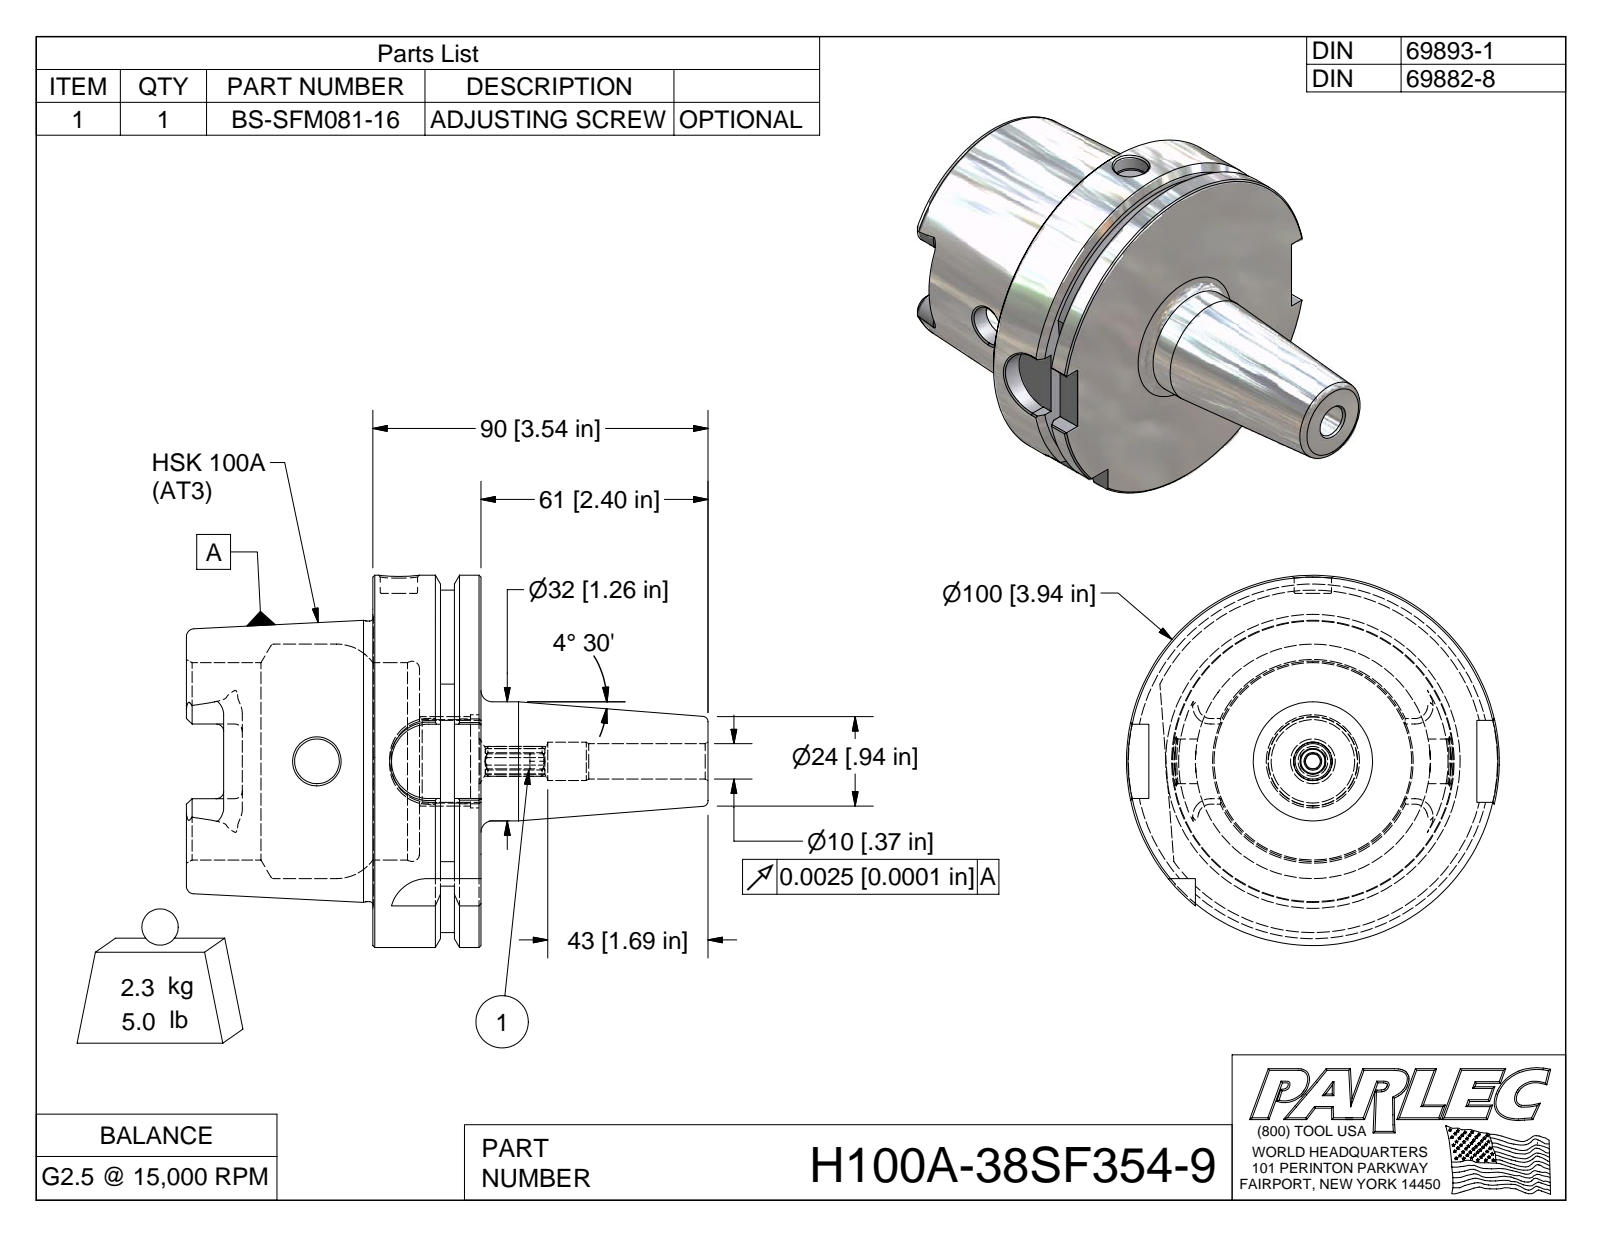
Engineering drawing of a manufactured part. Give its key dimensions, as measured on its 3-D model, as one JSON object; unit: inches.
{"part_name": "H100A-38SF354-9; H100A-38SF354-9-1; BS-SFM081-16", "step_written_by": "Autodesk Inventor 2009 (AUTOMOTIVE_DESIGN)", "units": "inches", "bodies": {"solids": 2, "faces": 149, "planar": 49, "cylindrical": 30, "other": 70}, "overall_size": [5.509, 3.937, 3.937], "volume_in3": 17.71, "surface_area_in2": 88.83, "round_holes": [[0.374, 1], [0.394, 1], [0.404, 1], [0.472, 1], [0.881, 1], [0.985, 1], [2.087, 1], [2.48, 1]], "round_bosses_or_shafts": [[3.937, 1], [2.967, 1], [1.26, 1]], "partial_cylinders_radius": [[0.394, 4], [0.079, 3], [0.192, 2], [0.157, 1], [1.811, 1]], "face_to_face_distances": [1.142, 0.492, 0.65, 1.969, 2.461, 3.11, 2.682, 0.713, 0.221, 0.428]}
